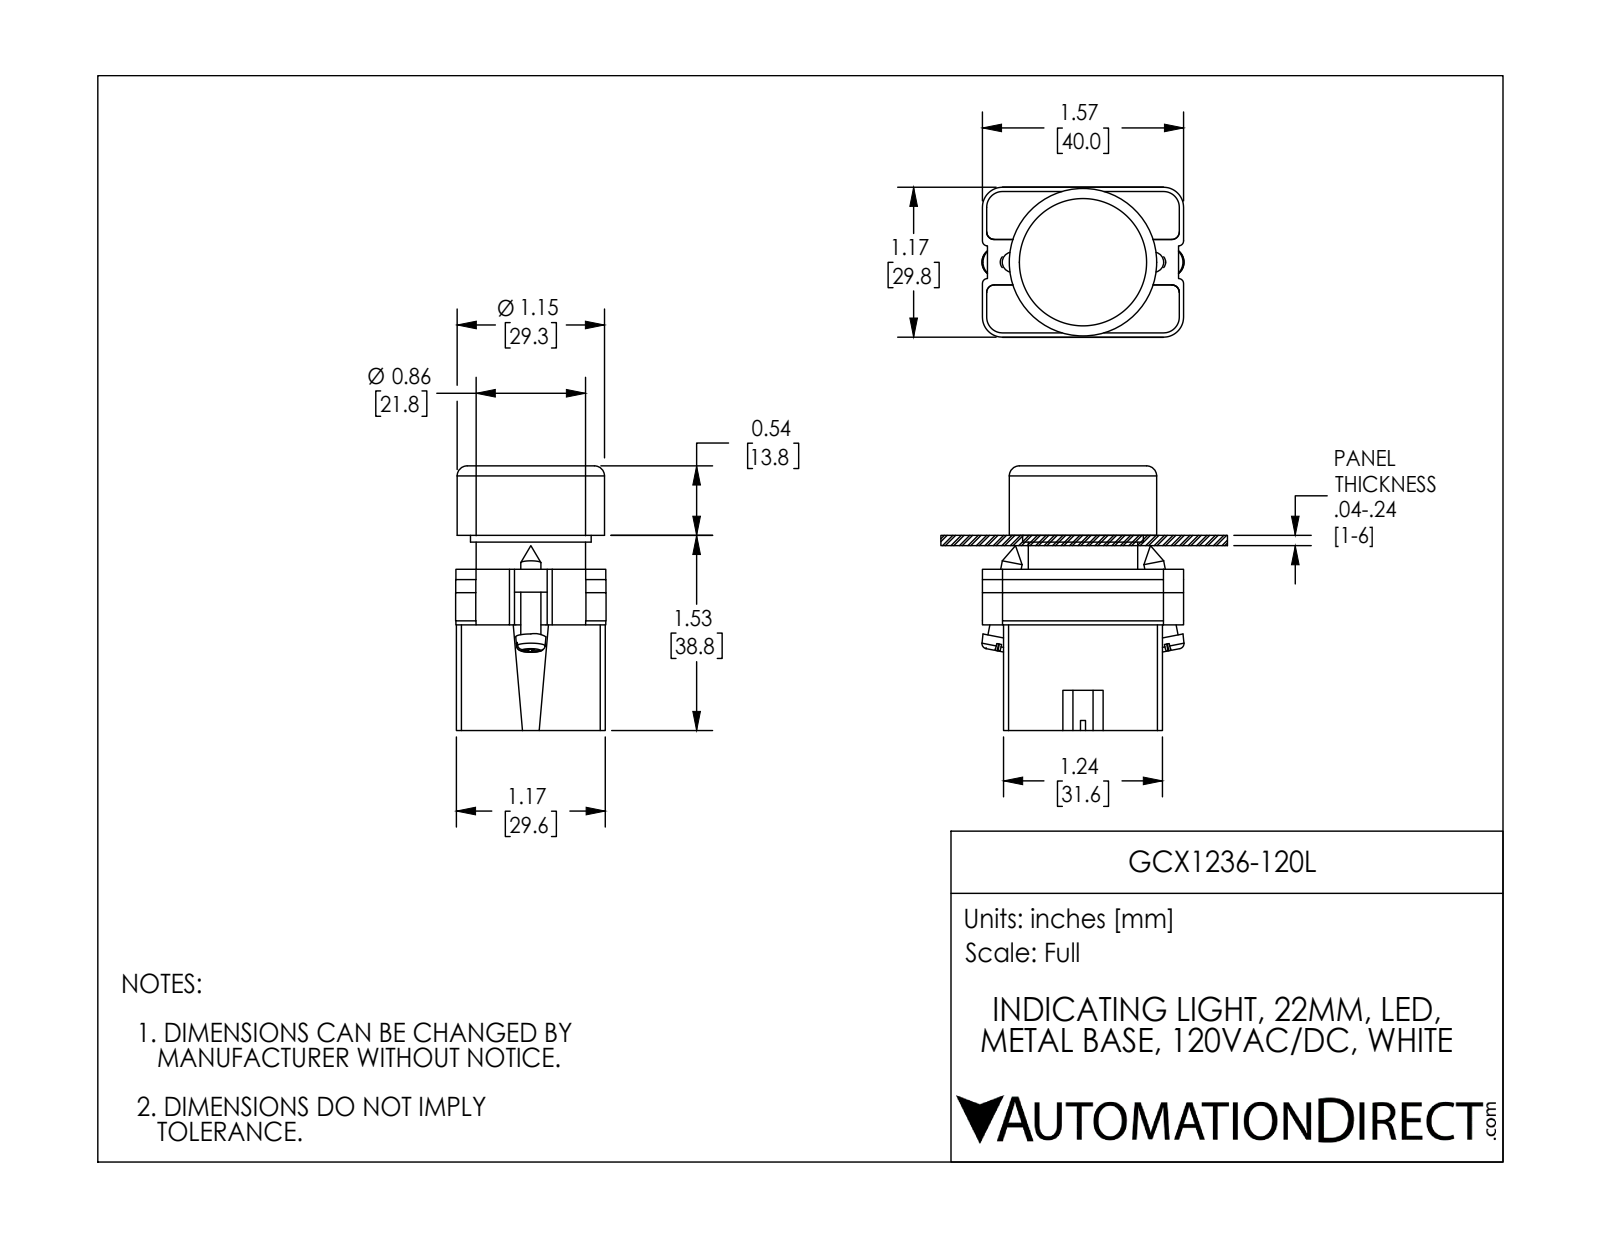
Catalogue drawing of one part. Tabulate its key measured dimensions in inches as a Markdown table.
| quantity | value |
| --- | --- |
| part name | ecx1029; GCX1236-120L; ECX1050; GCX1236L OPERATOR |
| STEP written by | SolidWorks 2016 (AUTOMOTIVE_DESIGN) |
| units | inches |
| bodies | 7 solids, 339 faces (178 planar, 134 cylindrical, 27 other) |
| overall size | 2.071 × 1.581 × 1.177 |
| volume | 2.268 in³ |
| surface area | 31.19 in² |
| round holes (diameter × count) | 0.124 × 2, 0.13 × 2, 0.197 × 1, 0.469 × 1, 0.852 × 1, 0.878 × 1, 0.888 × 1, 1.102 × 1 |
| round bosses / shafts (diameter × count) | 0.157 × 4, 1.154 × 1, 1.092 × 1, 0.945 × 1, 0.856 × 1, 0.78 × 1, 0.504 × 1 |
| partial cylindrical surfaces (radius × count) | 0.059 × 24, 0.041 × 12, 0.124 × 12, 0.157 × 12, 0.039 × 8, 0.128 × 2, 0.392 × 1, 0.398 × 1 |
| main face-to-face distances | 0.86, 1.244, 0.827, 1.687, 1.136, 0.033, 1.963, 0.276, 0.031, 1.165 |
